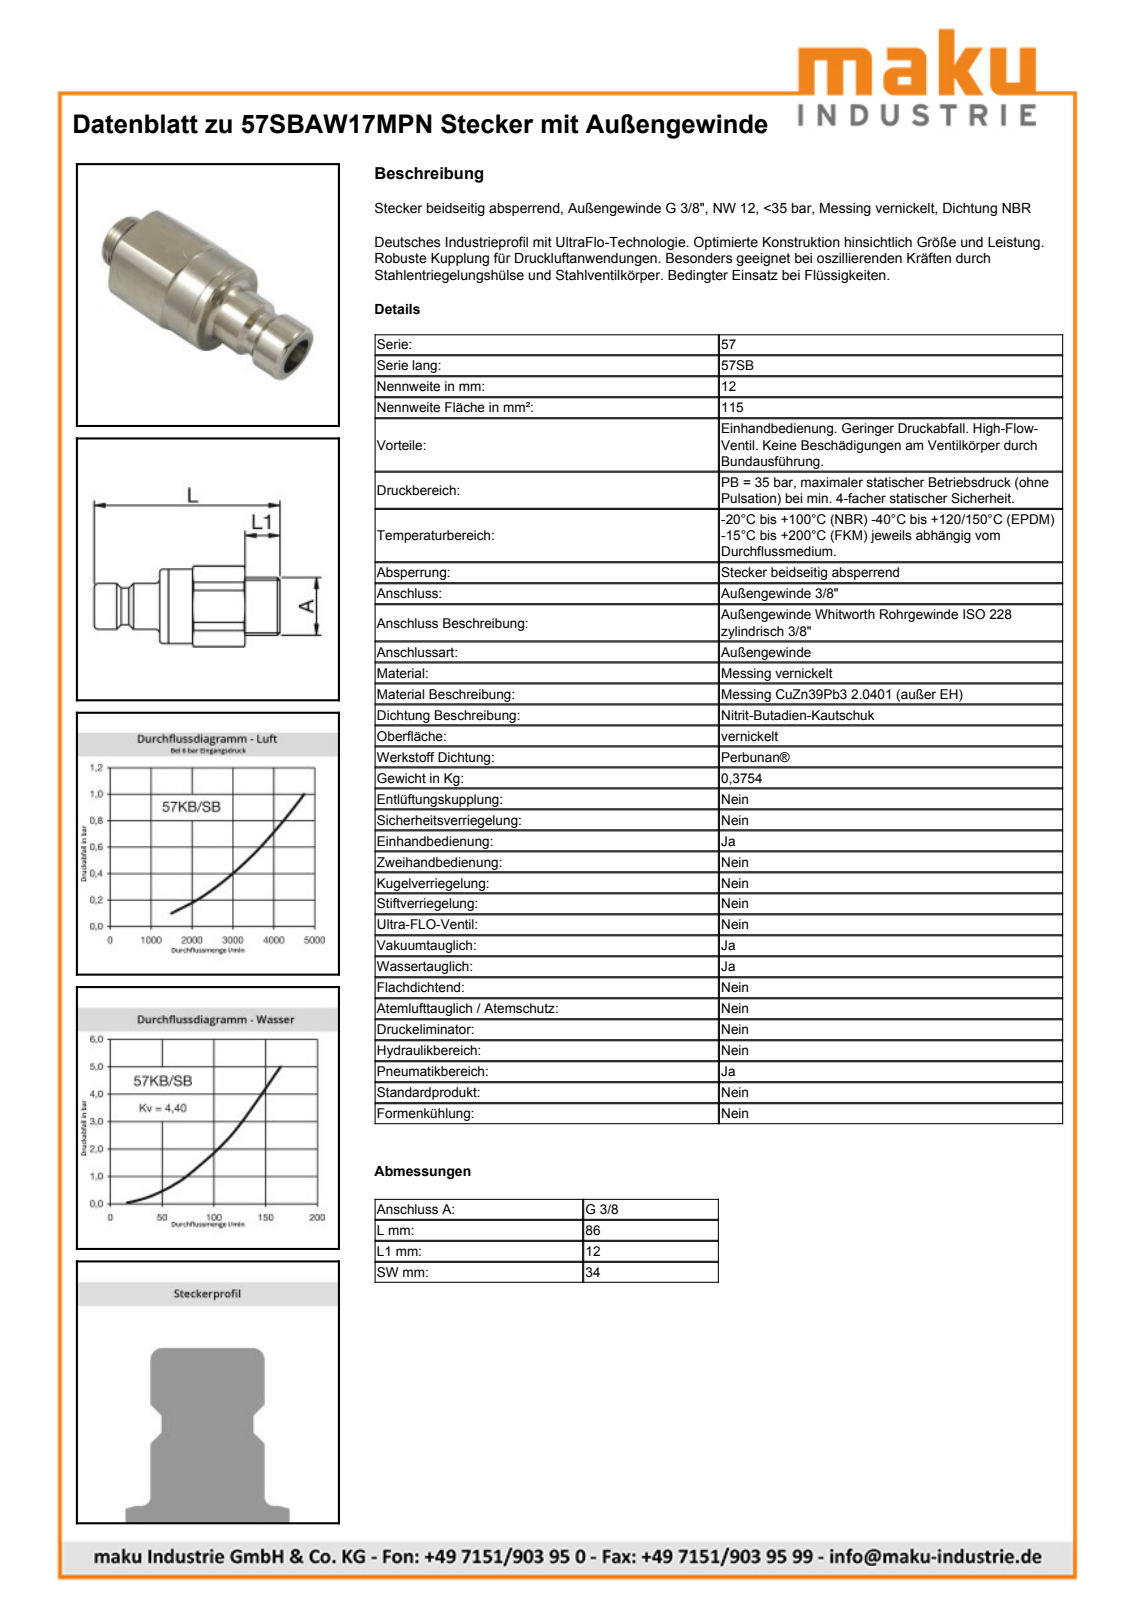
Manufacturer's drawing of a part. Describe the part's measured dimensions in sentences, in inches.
The part is named "D107533". Its 3-D file was written by "Autodesk Inventor 2013 (AUTOMOTIVE_DESIGN)". It is 1 solid with 43 faces: 11 planar, 12 cylindrical and 20 other. Overall it measures 3.386 by 1.456 by 1.408 inches. Its volume is 3.317 cubic inches and its surface area 14.55 square inches. Round bosses or shafts: 1 of diameter 1.339, 1 of diameter 1.144, 1 of diameter 0.823, 1 of diameter 0.661, 1 of diameter 0.656. Partial cylindrical surfaces (rounded edges, fillets, slot ends): 1 of radius 0.728. The main face-to-face distances are 1.339, 1.339, 1.732, 1.181, 2.913, 3.386, 2.205, 0.472, 0.157, 1.575.
